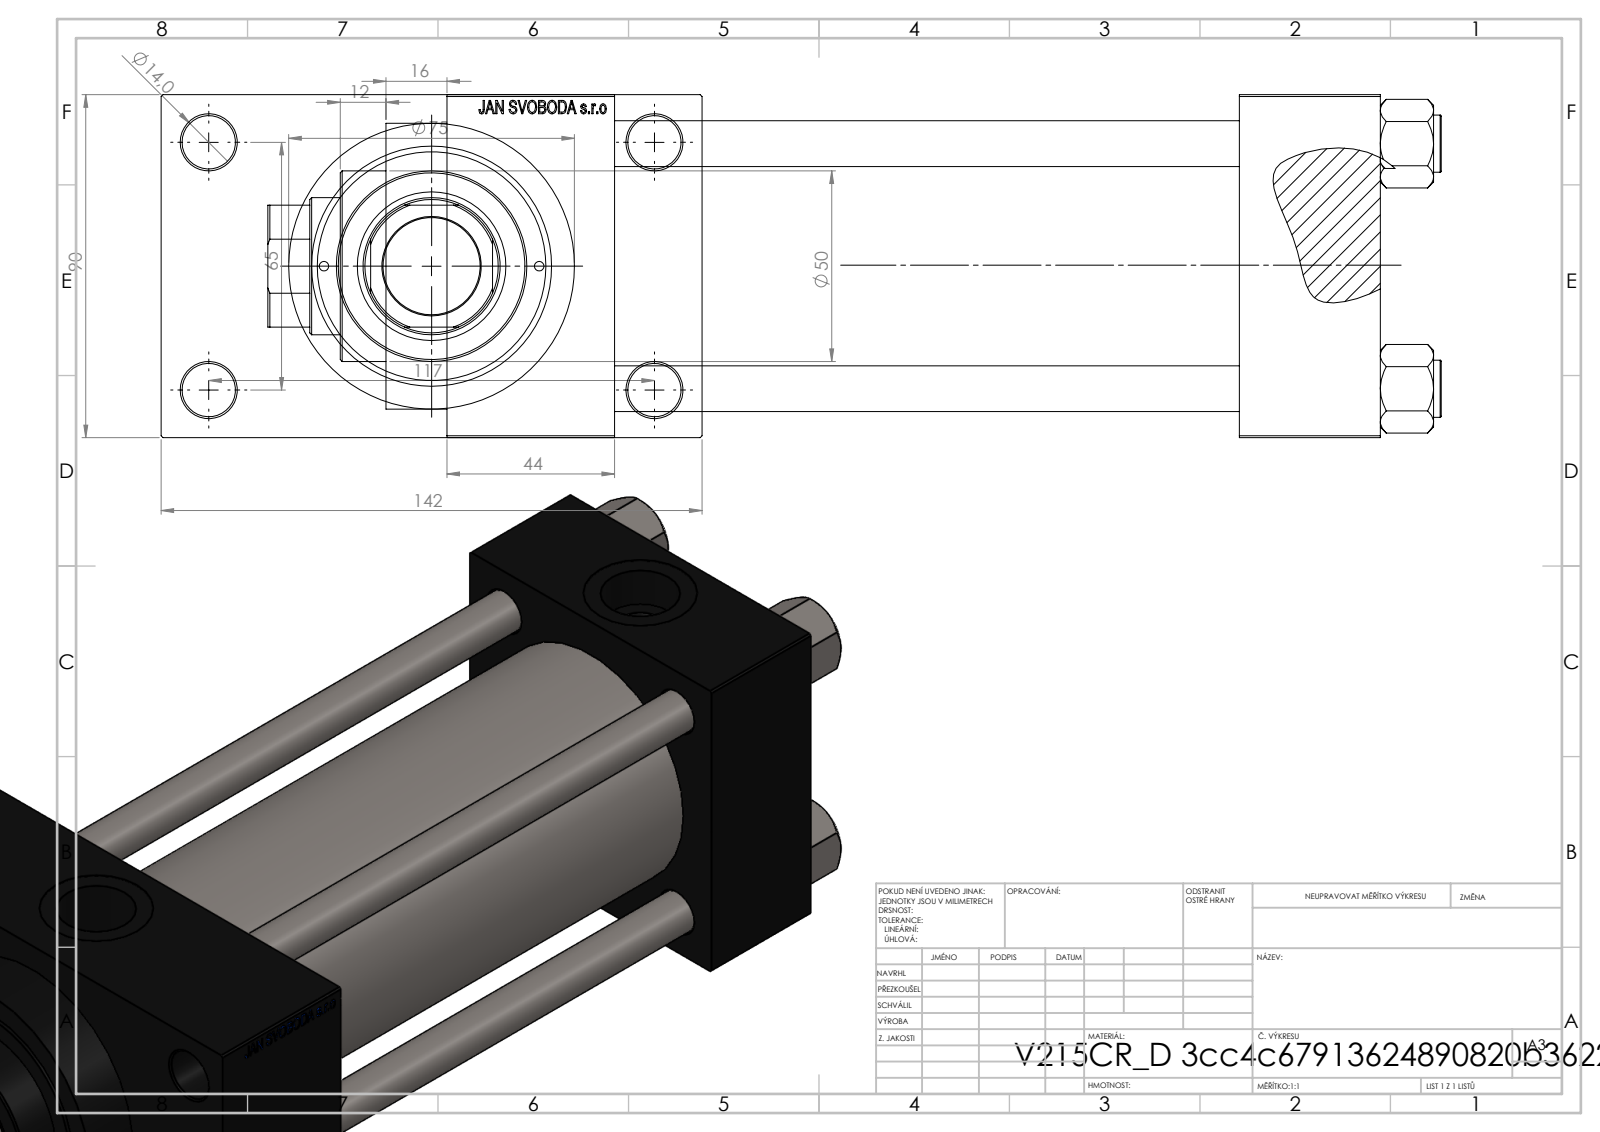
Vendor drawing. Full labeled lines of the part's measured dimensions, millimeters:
Part name (STEP PRODUCT): NUT_M5_D; V215CR_VCP_D; V215_VC_A; V215CR_D_TYCINKA (+1 more)
STEP written by: SolidWorks 2019 (CONFIG_CONTROL_DESIGN)
Units: millimetres
Bodies: 11 solids, 1112 faces (499 planar, 93 cylindrical, 520 other)
Overall size (bounding box): 308 × 142 × 90
Volume: 1 340 000 mm³ · Surface area: 275 244 mm²
Round holes (diameter × count): ⌀12 ×4, ⌀14 ×4, ⌀2.5 ×2, ⌀7 ×2, ⌀20.96 ×2, ⌀30 ×2, ⌀25.5 ×1, ⌀36 ×1, ⌀39 ×1, ⌀50 ×1, ⌀60 ×1, ⌀63 ×1
Round bosses / shafts (diameter × count): ⌀15 ×4, ⌀75 ×1, ⌀69 ×1
Partial cylindrical surfaces — rounded edges, fillets, slot ends (radius × count): R17.5 ×1
Main face-to-face distances: 90, 164, 37, 201, 245, 208, 44, 26, 116, 142
Hole centre spacings: 26.35, 32.39, 44.4, 45.47, 64.3, 66.92, 68.42, 69.81
